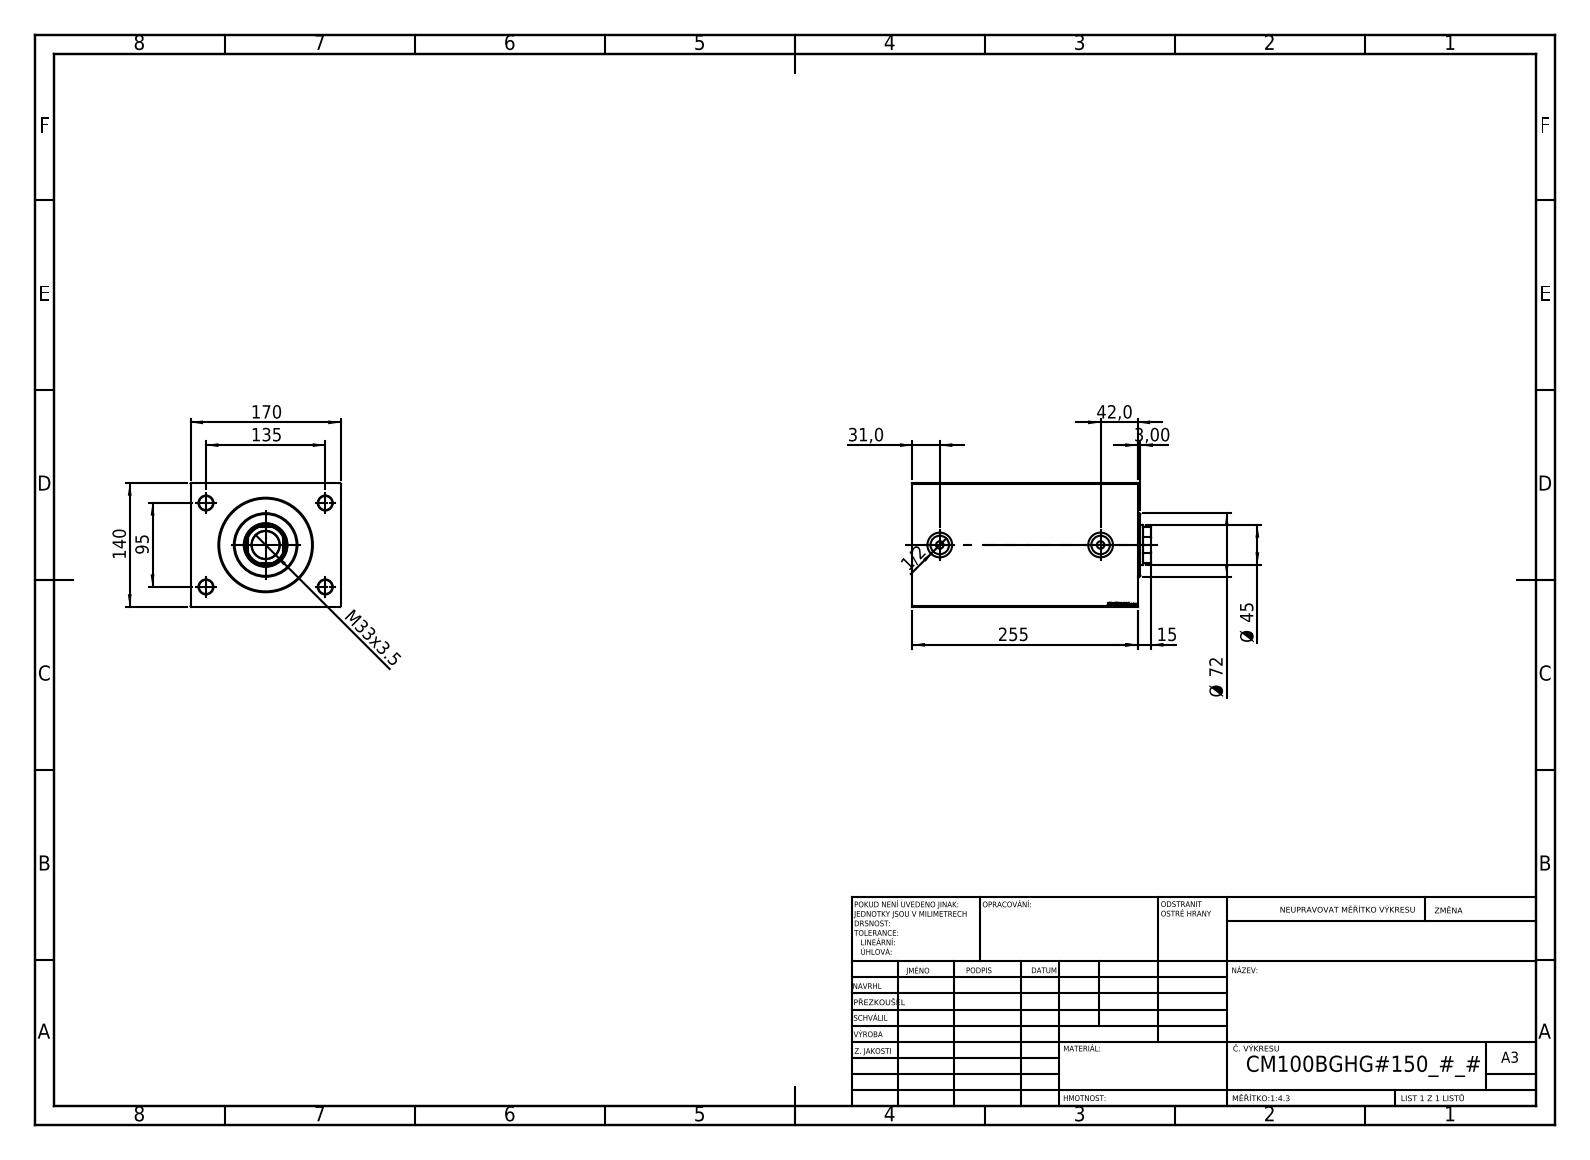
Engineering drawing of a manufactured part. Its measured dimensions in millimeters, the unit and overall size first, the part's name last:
Units: millimetres
Overall size (bounding box): 270 × 170 × 140
Round holes (diameter × count): ⌀16 ×4, ⌀8.5 ×2, ⌀20.96 ×2, ⌀28 ×2, ⌀31.5 ×1, ⌀45 ×1, ⌀48.5 ×1, ⌀49.5 ×1, ⌀100 ×1, ⌀102 ×1, ⌀105 ×1
Round bosses / shafts (diameter × count): ⌀72 ×1
Partial cylindrical surfaces — rounded edges, fillets, slot ends (radius × count): R22 ×1
Main face-to-face distances: 140, 170, 255, 229, 26, 15, 214, 240, 90, 64
Hole centre spacings: 82.54, 95, 135, 165.08, 182
Volume: 5 064 000 mm³ · Surface area: 379 459 mm²
Bodies: 3 solids, 884 faces (402 planar, 56 cylindrical, 426 other)
Part name (STEP PRODUCT): V450CM_B_Body; V450CM_VC_B; V450CM_B_VCP
STEP written by: SolidWorks 2019 (CONFIG_CONTROL_DESIGN)
